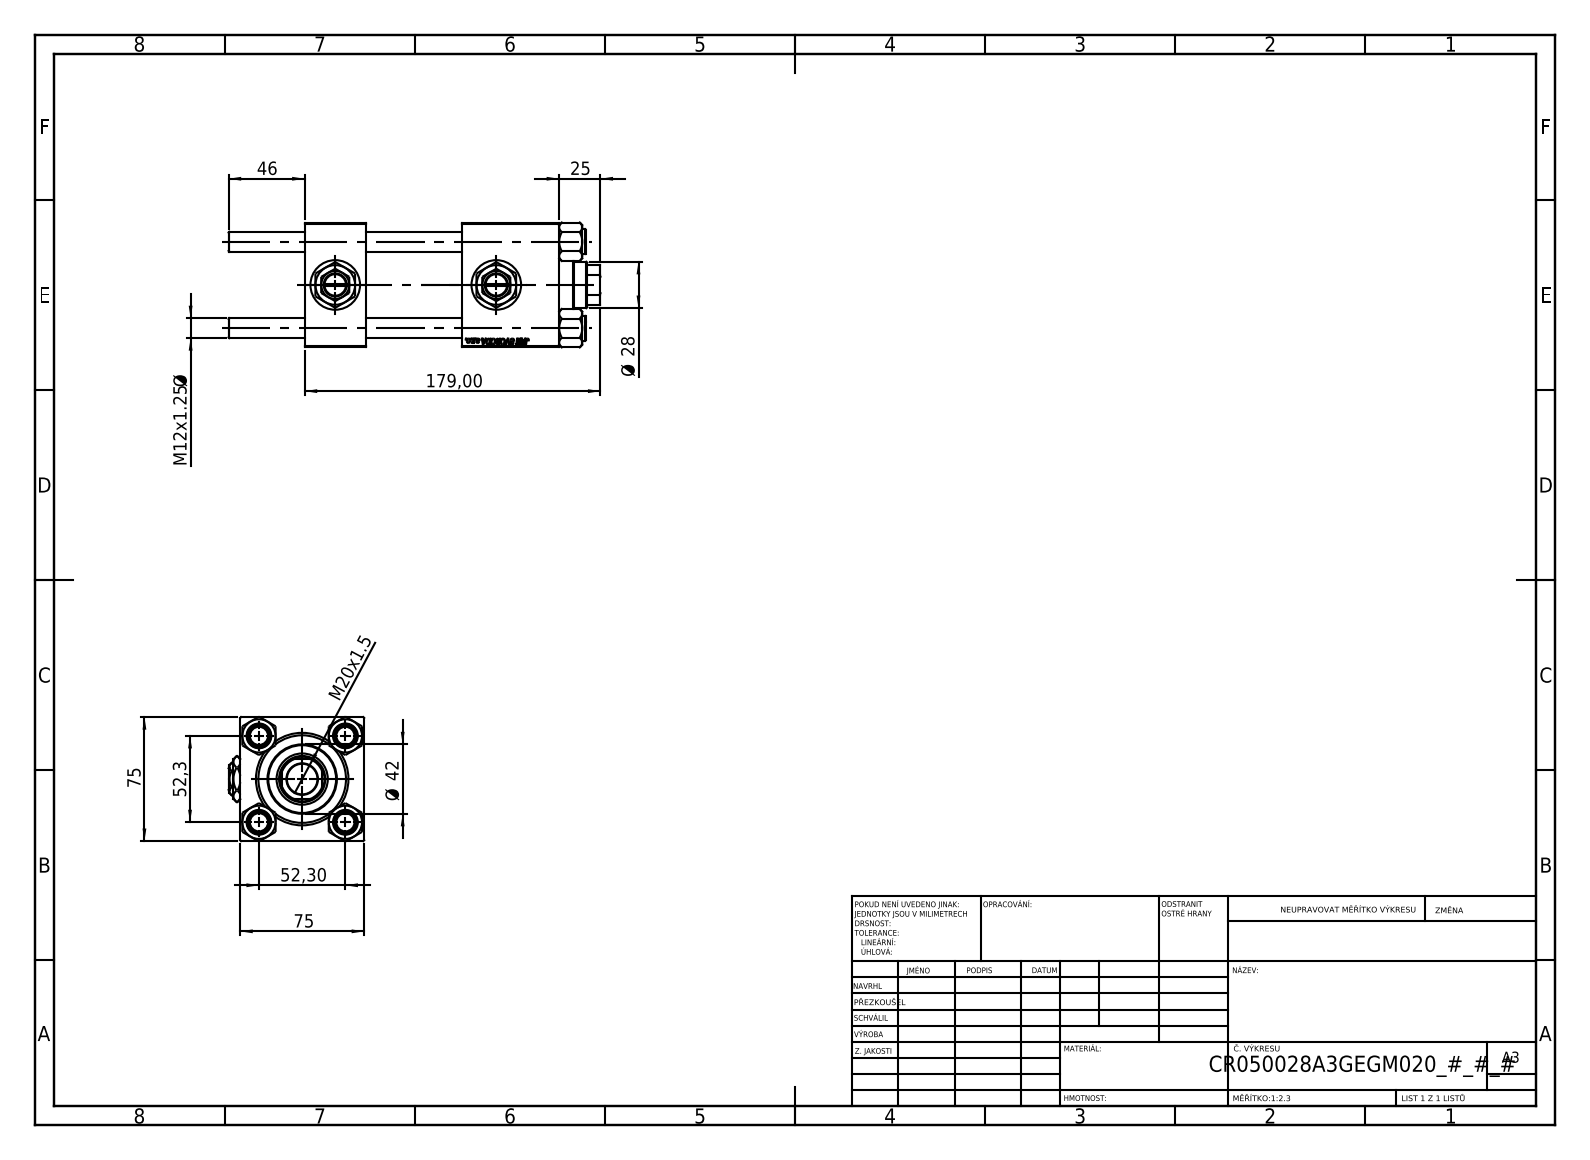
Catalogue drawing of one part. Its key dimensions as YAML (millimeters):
part_name: "NUT_M5; V215CR_BODY_A; V215_VC_A; Zatka_pro_OIL_PORT (+2 more)"
step_written_by: "SolidWorks 2019 (CONFIG_CONTROL_DESIGN)"
units: millimeters
bodies: {solids: 13, faces: 1235, planar: 567, cylindrical: 90, other: 578}
overall_size: [225, 82, 75.54]
volume: 696887
surface_area: 171606
round_holes:
  - {diameter: 12, count: 4}
  - {diameter: 20.96, count: 3}
  - {diameter: 30, count: 3}
  - {diameter: 7, count: 2}
  - {diameter: 17, count: 1}
  - {diameter: 18.5, count: 1}
  - {diameter: 28, count: 1}
  - {diameter: 31, count: 1}
  - {diameter: 41, count: 1}
  - {diameter: 50, count: 1}
  - {diameter: 53, count: 1}
round_bosses_or_shafts:
  - {diameter: 15, count: 4}
  - {diameter: 56, count: 1}
  - {diameter: 42, count: 1}
partial_cylinders:
  - {radius: 13.5, count: 1}
face_to_face_distances: [75, 37, 154, 117, 95, 59, 58, 74.8, 125.3, 88.3]
hole_center_spacings: [36.98, 52.3, 73.96, 3.96, 93.5, 97.46]
